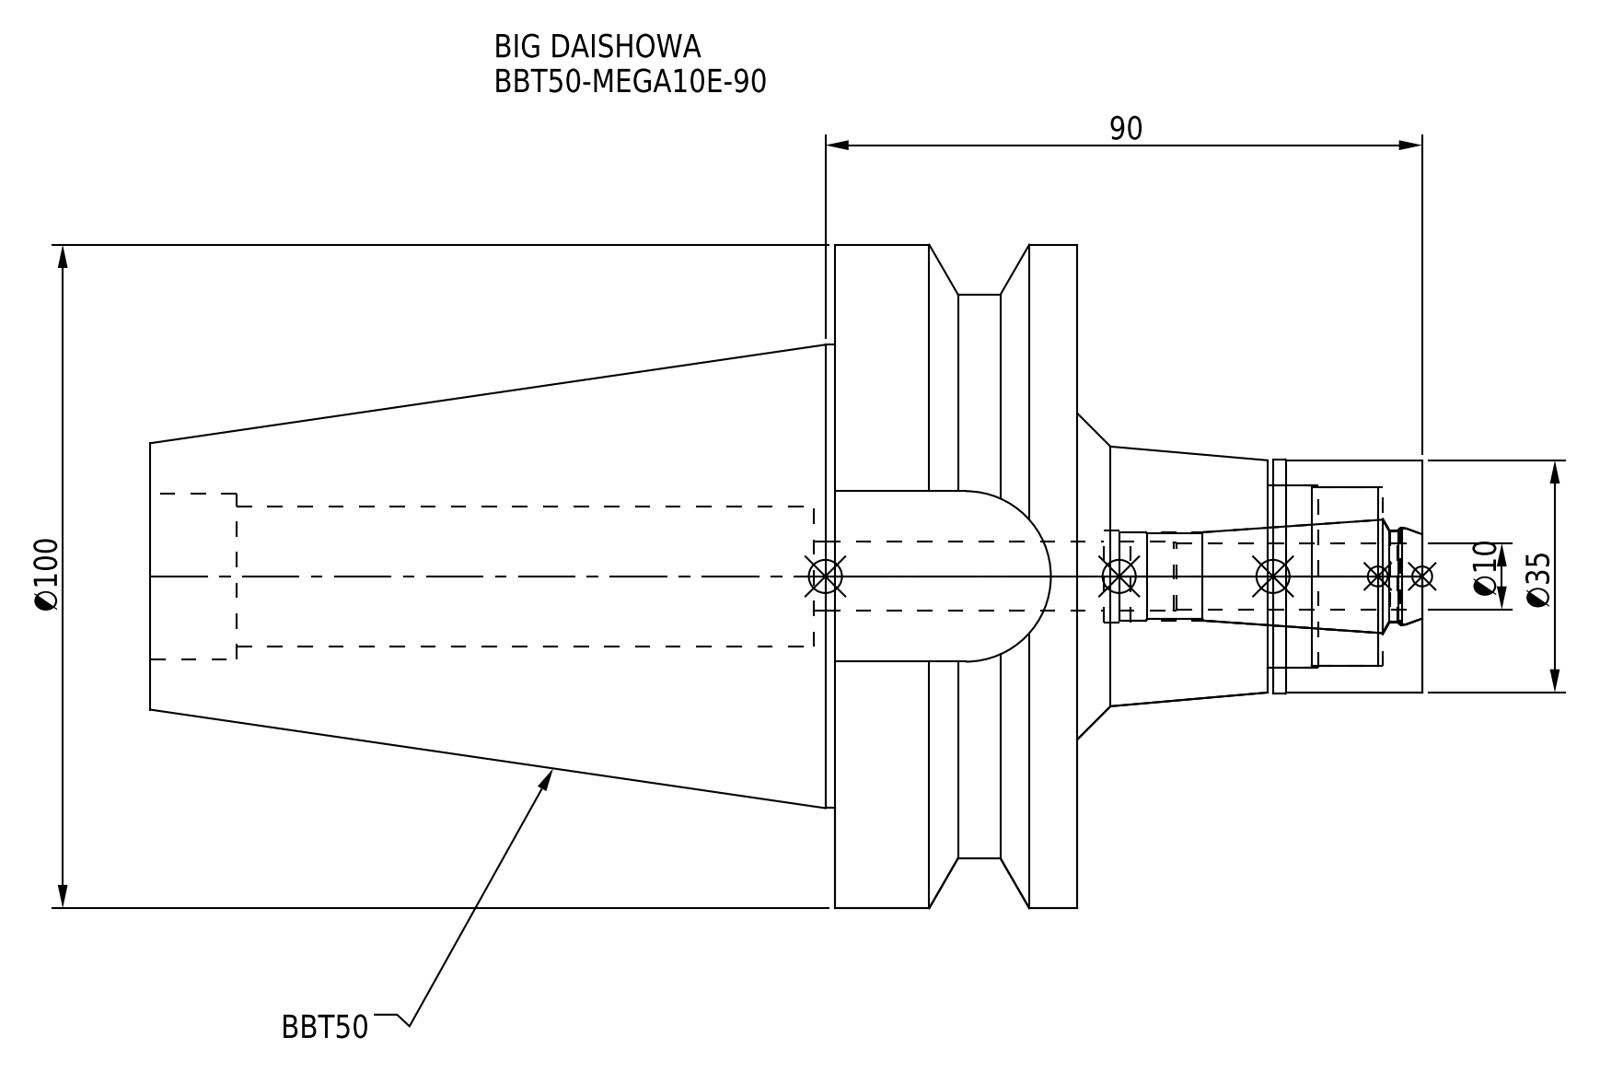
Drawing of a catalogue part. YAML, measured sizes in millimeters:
part_name: "BBT50ME10090-100_ASM.stp; MEN10_1.stp; BBT50-MEGA10E-90-100-FreeParts; DXF_TEMP_ASSY_ASM_4_ASM.stp (+3 more)"
step_written_by: "SolidWorks 2019 (CONFIG_CONTROL_DESIGN)"
units: millimeters
bodies: {solids: 2, faces: 78, planar: 20, cylindrical: 38, other: 20}
overall_size: [191.8, 100, 100]
volume: 505335
surface_area: 65296
round_holes:
  - {diameter: 10.4, count: 1}
  - {diameter: 13.3, count: 1}
  - {diameter: 13.8, count: 1}
  - {diameter: 13.9, count: 1}
  - {diameter: 14.7, count: 1}
  - {diameter: 21.2, count: 1}
  - {diameter: 25, count: 1}
  - {diameter: 27, count: 1}
  - {diameter: 27.5, count: 1}
round_bosses_or_shafts:
  - {diameter: 100, count: 1}
  - {diameter: 85, count: 1}
  - {diameter: 69.85, count: 1}
  - {diameter: 35.3, count: 1}
  - {diameter: 35, count: 1}
partial_cylinders:
  - {radius: 12.85, count: 1}
face_to_face_distances: [36.5, 52, 88.5, 191.8, 139.8, 103.3, 70.8, 25.7, 22.5, 29.5]
